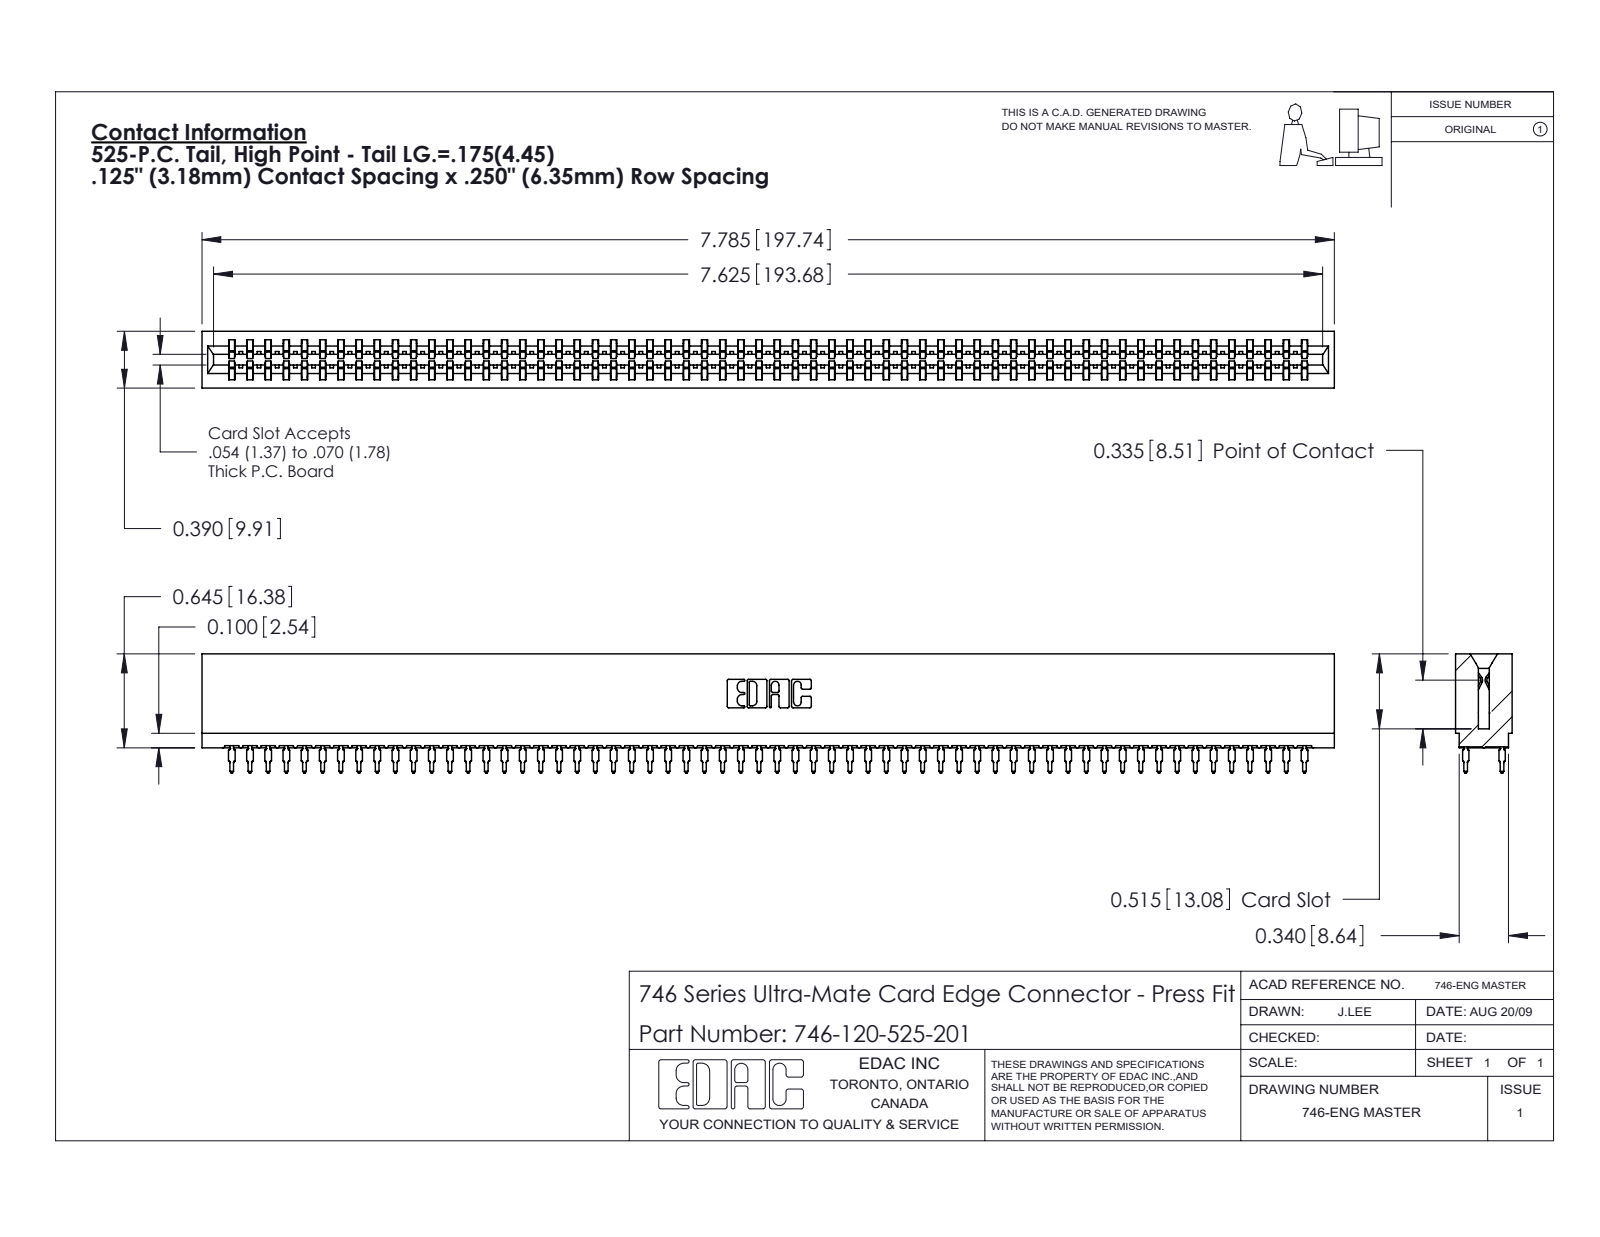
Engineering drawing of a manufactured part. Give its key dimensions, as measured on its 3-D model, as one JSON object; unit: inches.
{"part_name": "746-292-001_525; 746-120-525-201; 746 Part_.515 Slot Depth - 01", "step_written_by": "SolidWorks 2020 (CONFIG_CONTROL_DESIGN)", "units": "inches", "bodies": {"solids": 121, "faces": 10837, "planar": 5575, "cylindrical": 2142, "other": 3120}, "overall_size": [7.785, 0.819, 0.39], "volume_in3": 1.282, "surface_area_in2": 52.4, "partial_cylinders_radius": [[0.021, 240], [0.015, 61], [0.01, 22], [0.005, 8], [0.011, 8], [0.007, 6], [0.031, 6], [0.026, 3]], "face_to_face_distances": [0.057, 0.333, 0.39, 0.025, 0.25, 0.307, 0.275, 0.083, 0.174, 0.158]}
